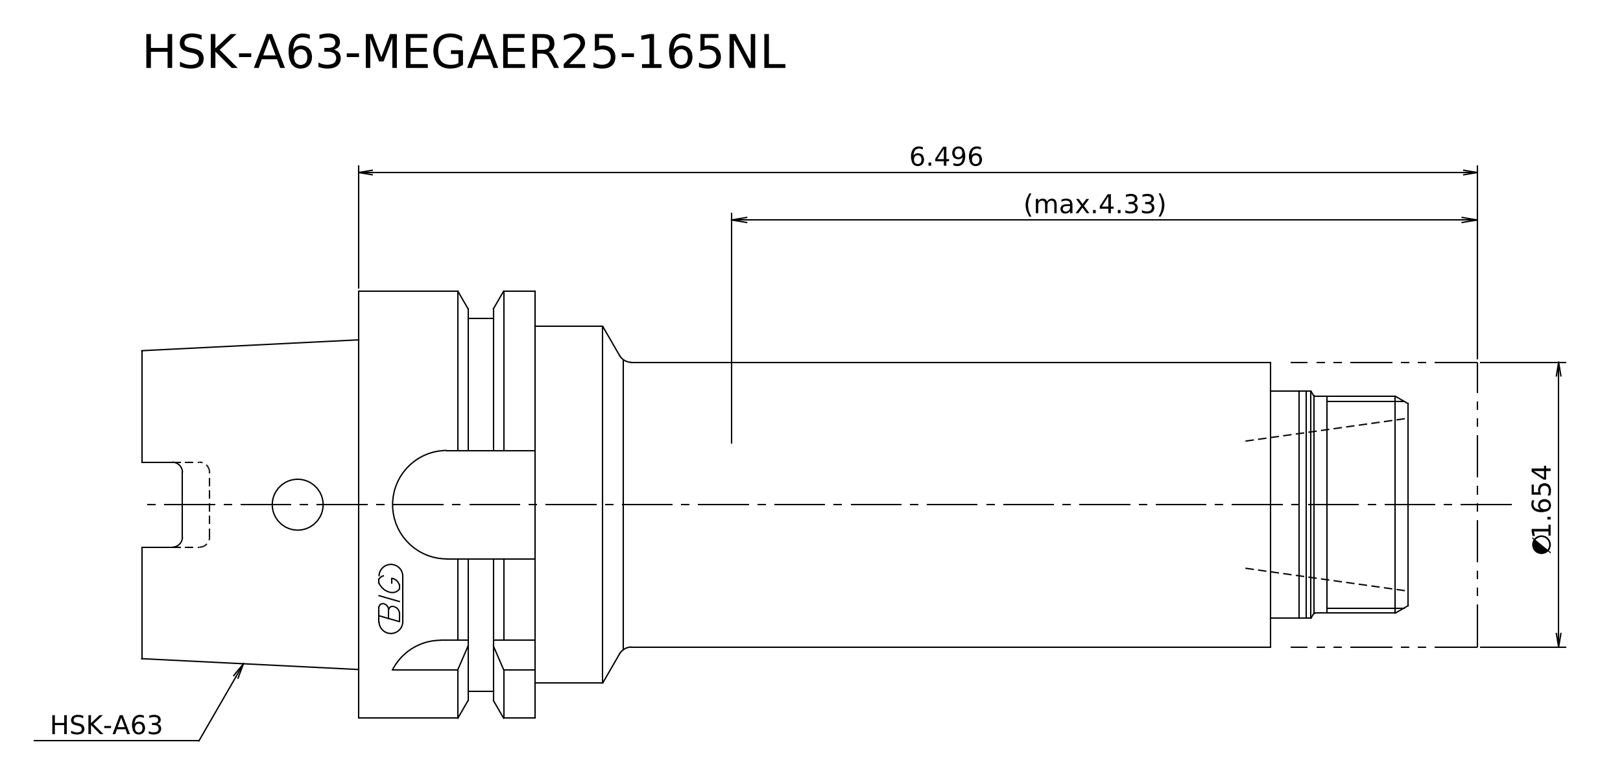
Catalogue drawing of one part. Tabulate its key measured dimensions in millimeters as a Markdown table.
| quantity | value |
| --- | --- |
| STEP written by | Kubotek KeyCreator 2011 V10.0.2 (22737) (automotive_design) |
| units | millimeters |
| bodies | 2 solids, 23 faces (9 planar, 8 cylindrical, 6 other) |
| overall size | 197 × 63 × 63 |
| volume | 347 729 mm³ |
| surface area | 39 479 mm² |
| round bosses / shafts (diameter × count) | 63 × 1, 55 × 1, 52.6 × 1, 42 × 1, 33.5 × 1, 32 × 1 |
| main face-to-face distances | 169.5, 27.5, 197, 165, 137.5, 32, 139, 111.5, 26, 58 |
